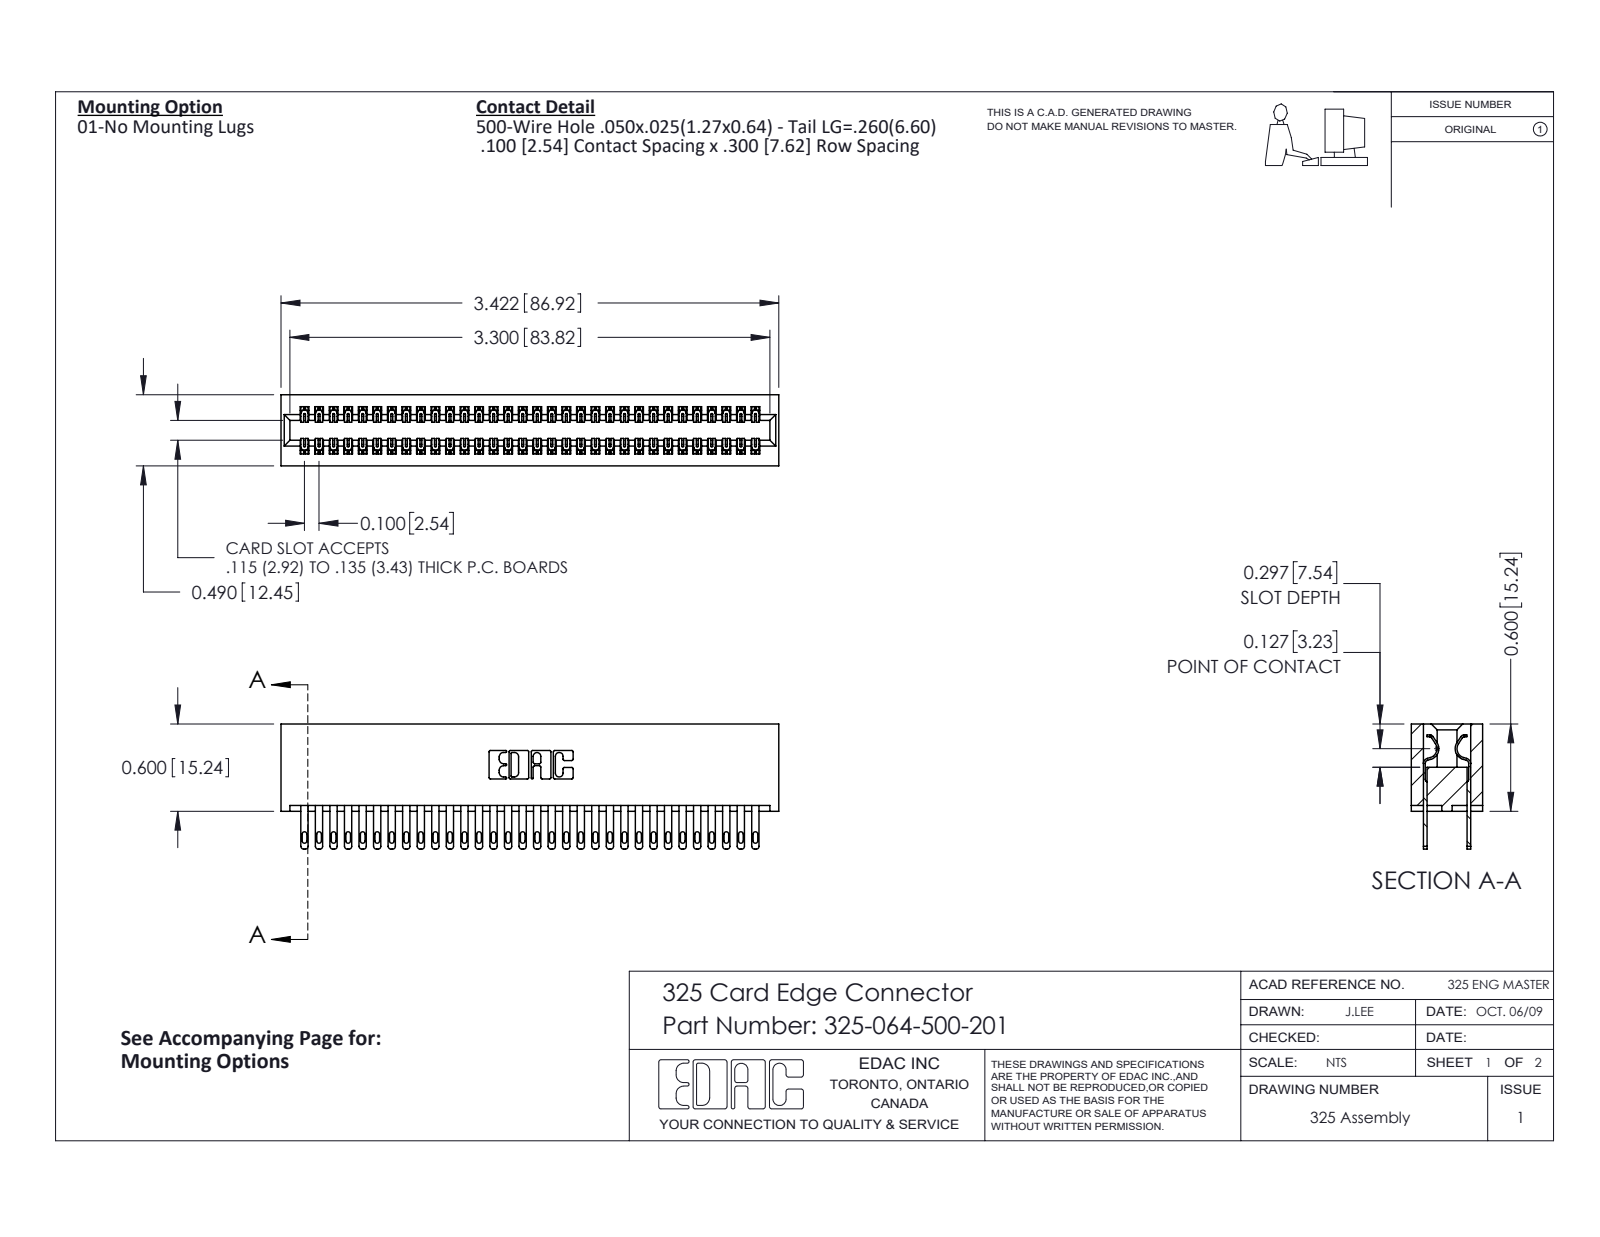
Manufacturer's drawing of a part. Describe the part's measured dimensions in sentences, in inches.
The part is named "325 Part_Lugless; 325-064-500-201; 325-292-001_325-293-100". Its 3-D file was written by "SolidWorks 2016 (CONFIG_CONTROL_DESIGN)". It is 65 solids with 3178 faces: 1986 planar, 1192 cylindrical and 0 other. Overall it measures 3.422 by 0.86 by 0.49 inches. Its volume is 0.728 cubic inches and its surface area 24.08 square inches. Partial cylindrical surfaces (rounded edges, fillets, slot ends): 96 of radius 0.006, 64 of radius 0.016, 64 of radius 0.02, 22 of radius 0.01, 6 of radius 0.007, 6 of radius 0.031, 3 of radius 0.026, 2 of radius 0.014. The main face-to-face distances are 0.083, 0.407, 0.3, 0.107, 0.383, 0.025, 0.325, 0.49, 0.275, 0.1.
